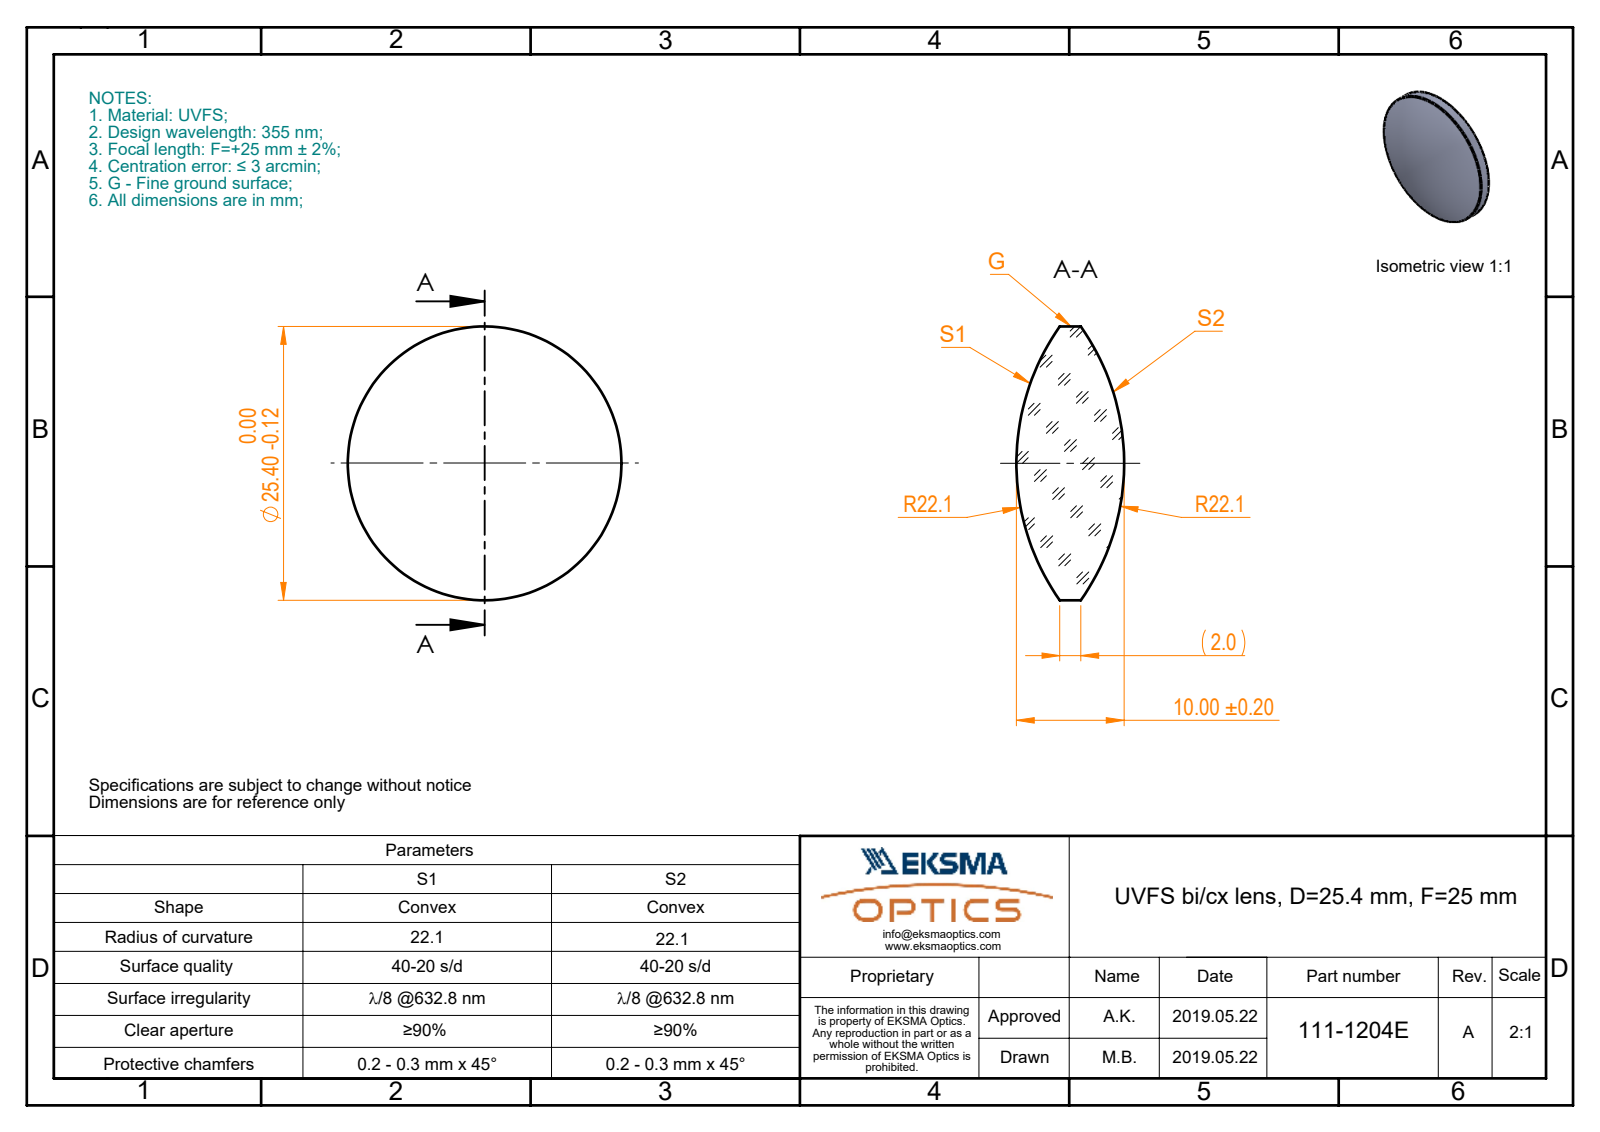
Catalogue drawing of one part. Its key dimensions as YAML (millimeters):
part_name: "111-1204E UVFS bi-cx 25.4 F25"
step_written_by: "SolidWorks 2017 (CONFIG_CONTROL_DESIGN)"
units: millimeters
bodies: {solids: 1, faces: 6, planar: 0, cylindrical: 2, other: 4}
overall_size: [25.4, 25.4, 10]
volume: 3097
surface_area: 1271
round_bosses_or_shafts:
  - {diameter: 25.4, count: 1}
